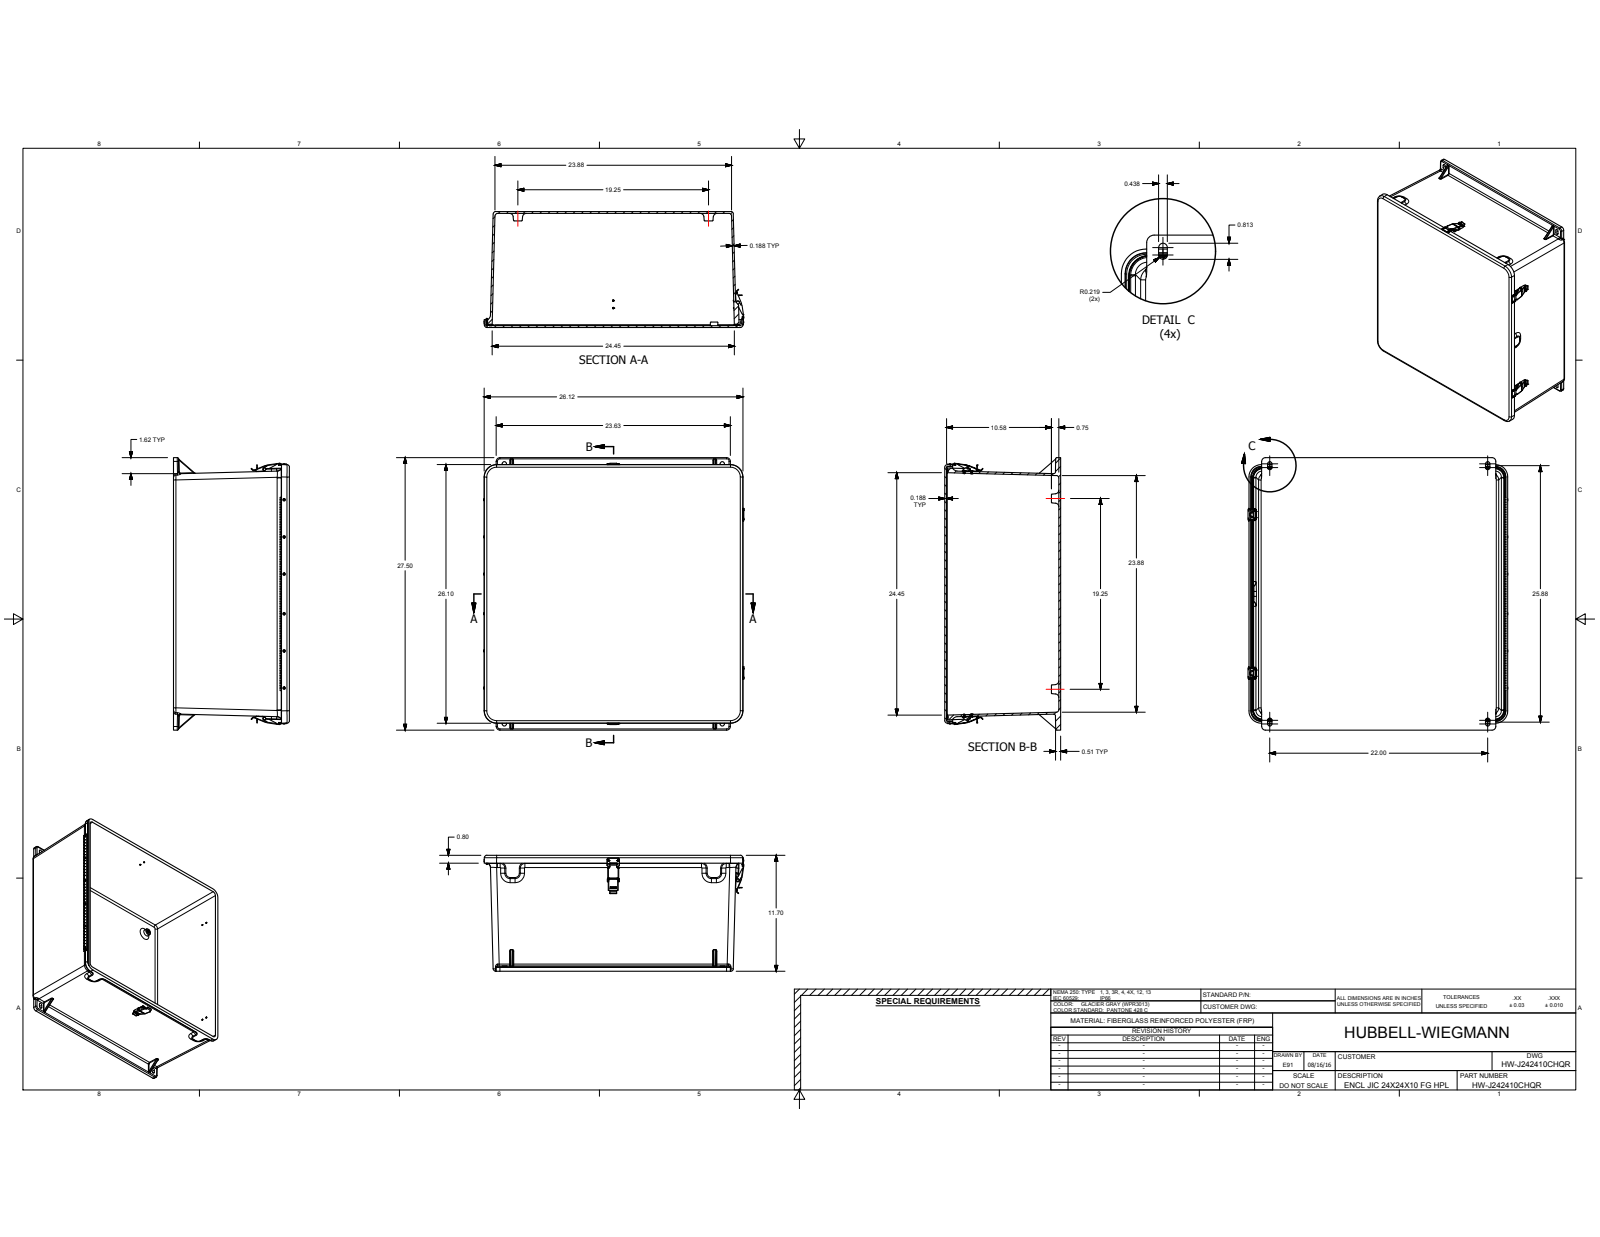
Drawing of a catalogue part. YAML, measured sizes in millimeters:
part_name: "HW-J242410CHQR; WP2424H&LBOX; WP2424HLU; WP2424H&LCVR (+8 more)"
step_written_by: "Autodesk Inventor 2017 (CONFIG_CONTROL_DESIGN)"
units: millimeters
bodies: {solids: 62, faces: 2139, planar: 803, cylindrical: 878, other: 458}
overall_size: [698.5, 666.08, 297.2]
volume: 8624000
surface_area: 3408000
round_holes:
  - {diameter: 2.64, count: 28}
  - {diameter: 3.53, count: 24}
  - {diameter: 3.33, count: 12}
  - {diameter: 3.3, count: 8}
  - {diameter: 3.56, count: 8}
  - {diameter: 3.43, count: 6}
  - {diameter: 5.18, count: 4}
  - {diameter: 9.52, count: 4}
  - {diameter: 9.93, count: 4}
  - {diameter: 7.87, count: 2}
  - {diameter: 2.16, count: 1}
round_bosses_or_shafts:
  - {diameter: 3.17, count: 28}
  - {diameter: 7.62, count: 3}
  - {diameter: 4.31, count: 3}
  - {diameter: 3.05, count: 3}
  - {diameter: 3.94, count: 1}
partial_cylinders:
  - {radius: 0.13, count: 72}
  - {radius: 0.38, count: 44}
  - {radius: 3.17, count: 40}
  - {radius: 0.51, count: 35}
  - {radius: 1.14, count: 32}
  - {radius: 1.52, count: 30}
  - {radius: 0.76, count: 24}
  - {radius: 1.59, count: 20}
face_to_face_distances: [4.78, 292.43, 297.21, 287.65, 4.77, 641.65, 12.04, 290.53, 285.75, 1.9]
hole_center_spacings: [95.25, 190.5, 406.4, 279.4, 292.1, 0.34, 22.84, 184.15]
